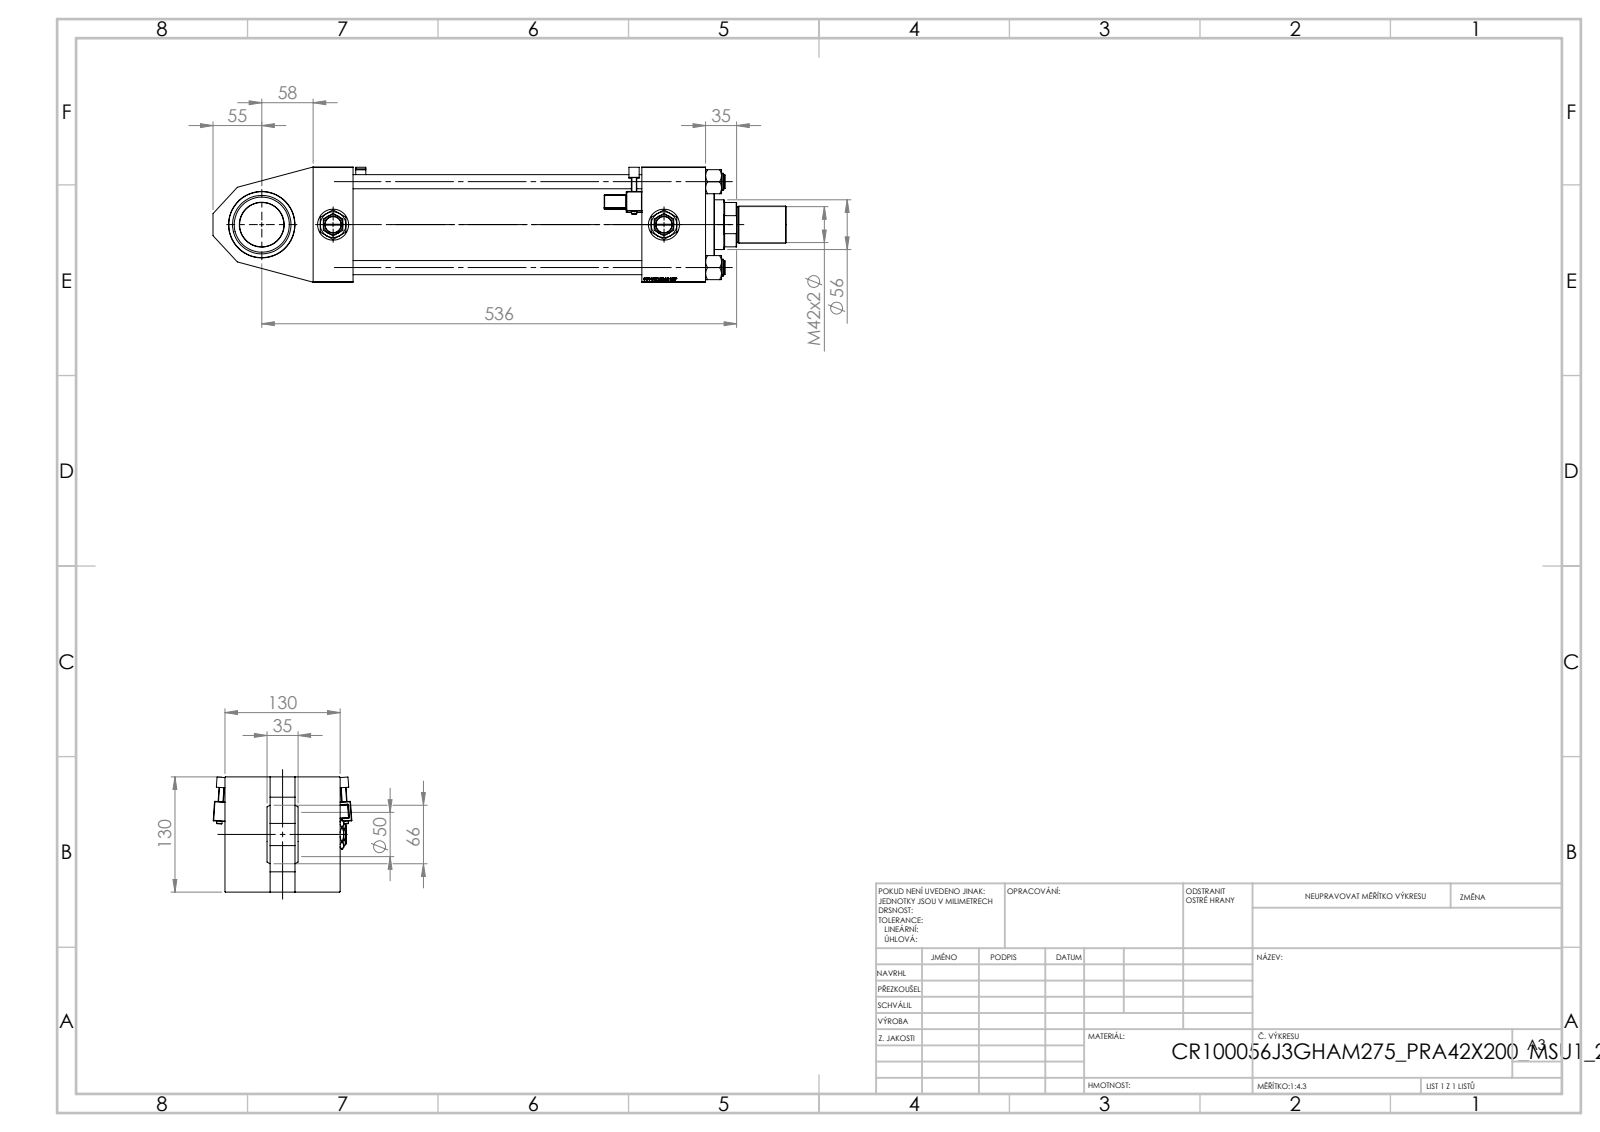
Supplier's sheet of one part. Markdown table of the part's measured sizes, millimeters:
| quantity | value |
| --- | --- |
| part name | Zatka_pro_OIL_PORT; V215CR_VCP_J; V215_VC_A; V215CR_J_Body (+5 more) |
| STEP written by | SolidWorks 2019 (CONFIG_CONTROL_DESIGN) |
| units | millimeters |
| bodies | 17 solids, 1462 faces (674 planar, 164 cylindrical, 624 other) |
| overall size | 647 × 156.39 × 130 |
| volume | 3 933 000 mm³ |
| surface area | 670 234 mm² |
| round holes (diameter × count) | 16 × 4, 2.5 × 2, 7 × 2, 26.44 × 2, 35 × 2, 40.5 × 1, 50 × 1, 56 × 1, 59 × 1, 75 × 1, 76 × 1, 85.5 × 1 |
| round bosses / shafts (diameter × count) | 19 × 4, 6 × 2, 106 × 1, 72 × 1, 42 × 1, 40 × 1 |
| partial cylindrical surfaces (radius × count) | 0.5 × 48, 1 × 2, 2.5 × 2, 4 × 2, 27 × 1 |
| main face-to-face distances | 130, 51, 79, 45, 443, 398, 371, 326, 72, 28 |
| hole center spacings | 49.02, 68.52, 96.9, 101.73, 41, 137.04, 80.5, 82 |
